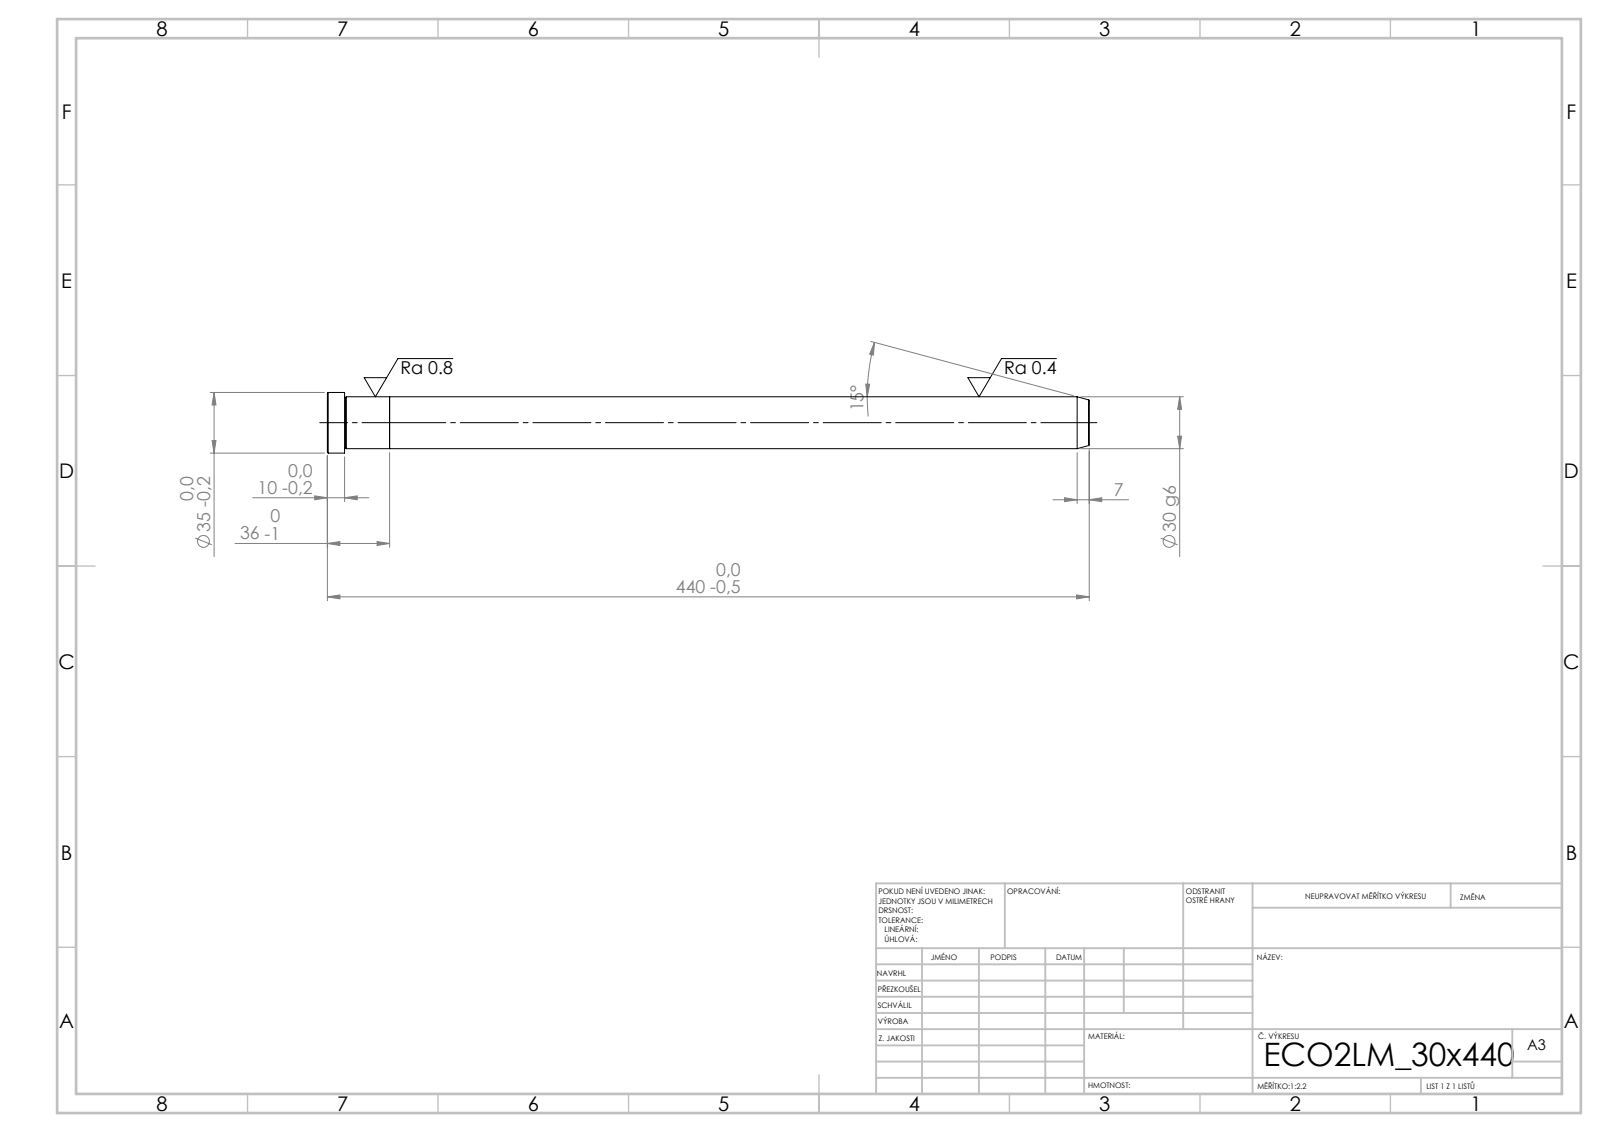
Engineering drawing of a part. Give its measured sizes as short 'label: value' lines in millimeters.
written by: SolidWorks 2019 (CONFIG_CONTROL_DESIGN)
unit: mm
bodies: 2 solids, 21 faces (5 planar, 6 cylindrical, 10 other)
size: 440 × 35 × 35
volume: 312 925 mm³; area: 44 788 mm²
bosses: 1× ⌀35, 1× ⌀30
face distances: 36, 404, 440, 430, 26, 10
